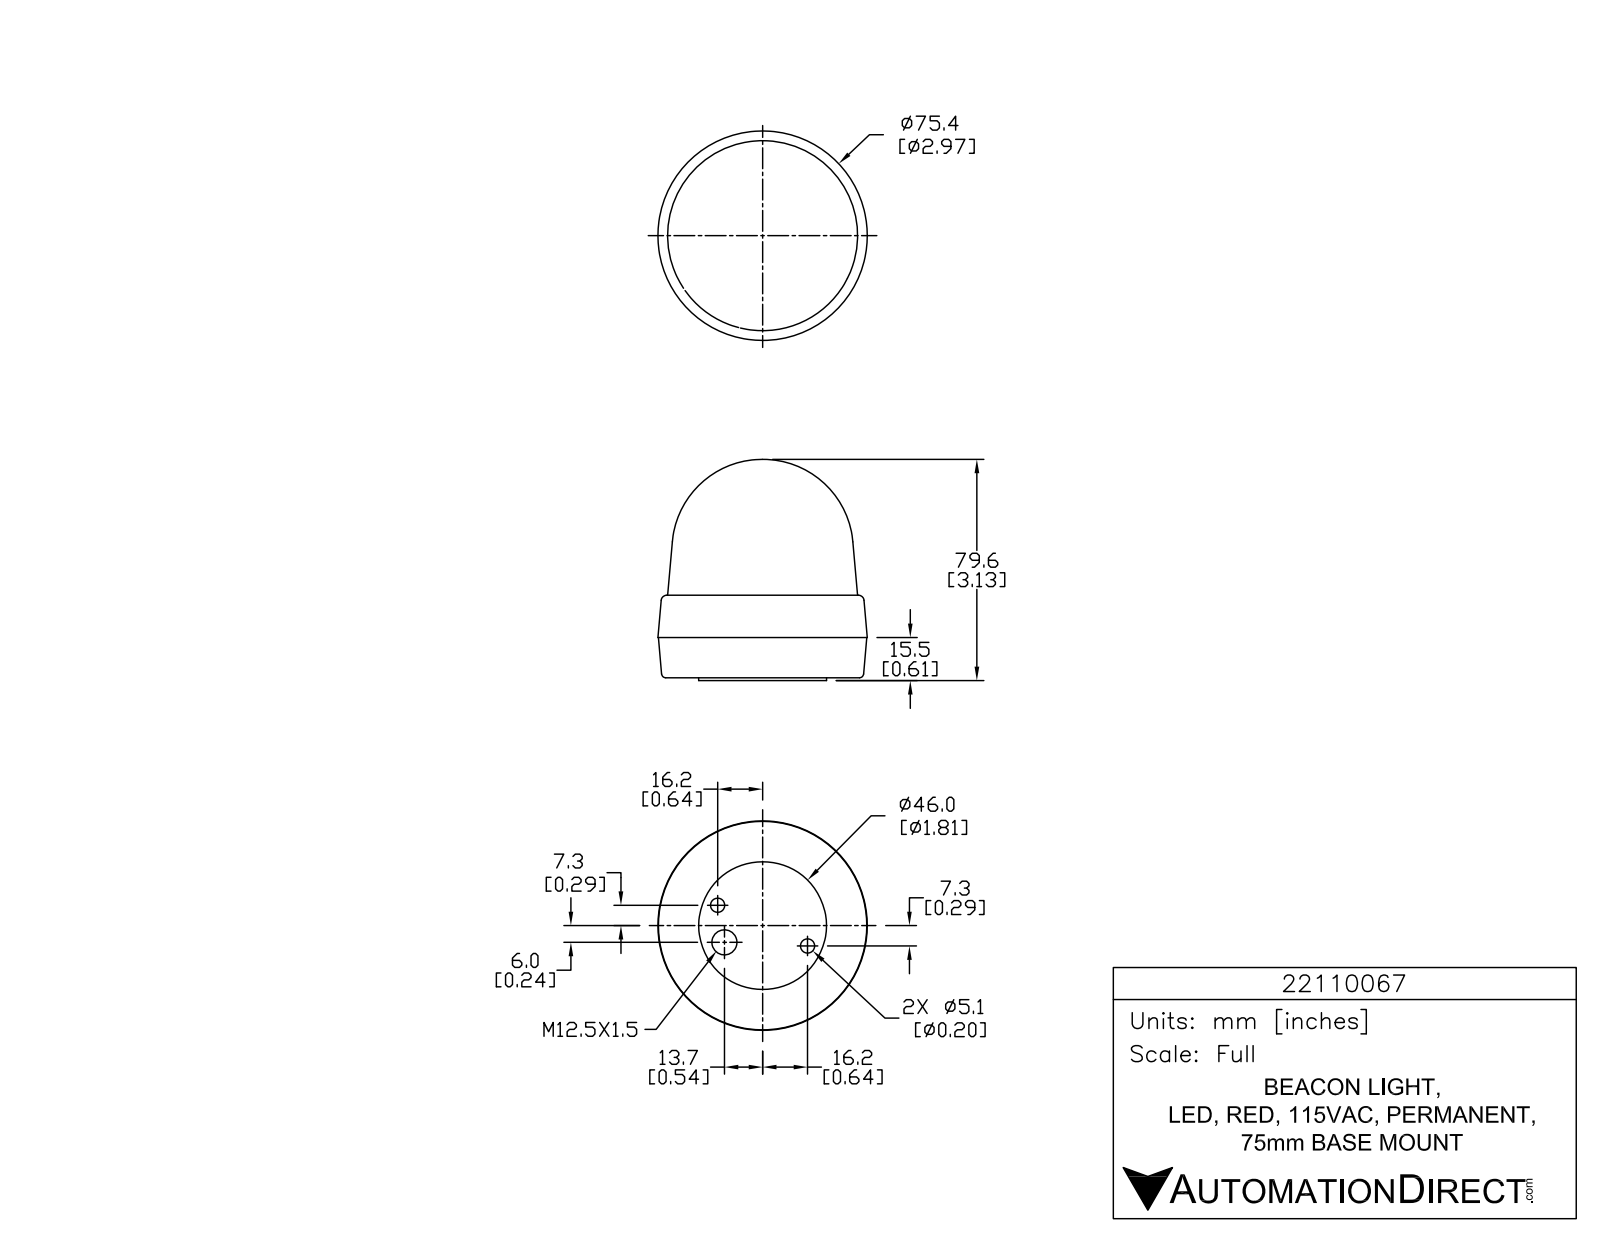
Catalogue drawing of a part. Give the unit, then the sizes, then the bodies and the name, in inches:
Units: inches
Overall size (bounding box): 3.133 × 2.967 × 2.967
Round holes (diameter × count): ⌀0.059 ×3, ⌀0.201 ×2, ⌀0.354 ×1
Round bosses / shafts (diameter × count): ⌀0.339 ×3, ⌀0.084 ×3, ⌀1.811 ×1
Partial cylindrical surfaces — rounded edges, fillets, slot ends (radius × count): R0.005 ×9, R0.005 ×6, R0.012 ×6, R0.012 ×6, R0.012 ×6, R0.196 ×6, R0.005 ×3, R0.005 ×3
Main face-to-face distances: 0.039, 1.209, 1.17, 0.61, 0.571, 0.599, 1.566, 1.527, 0.956, 0.357
Hole centre spacings: 0.534, 1.179, 1.398
Volume: 15.79 in³ · Surface area: 33.7 in²
Bodies: 1 solid, 773 faces (526 planar, 163 cylindrical, 84 other)
Part name (STEP PRODUCT): 22110067
STEP written by: SolidWorks 2015 (AUTOMOTIVE_DESIGN)
